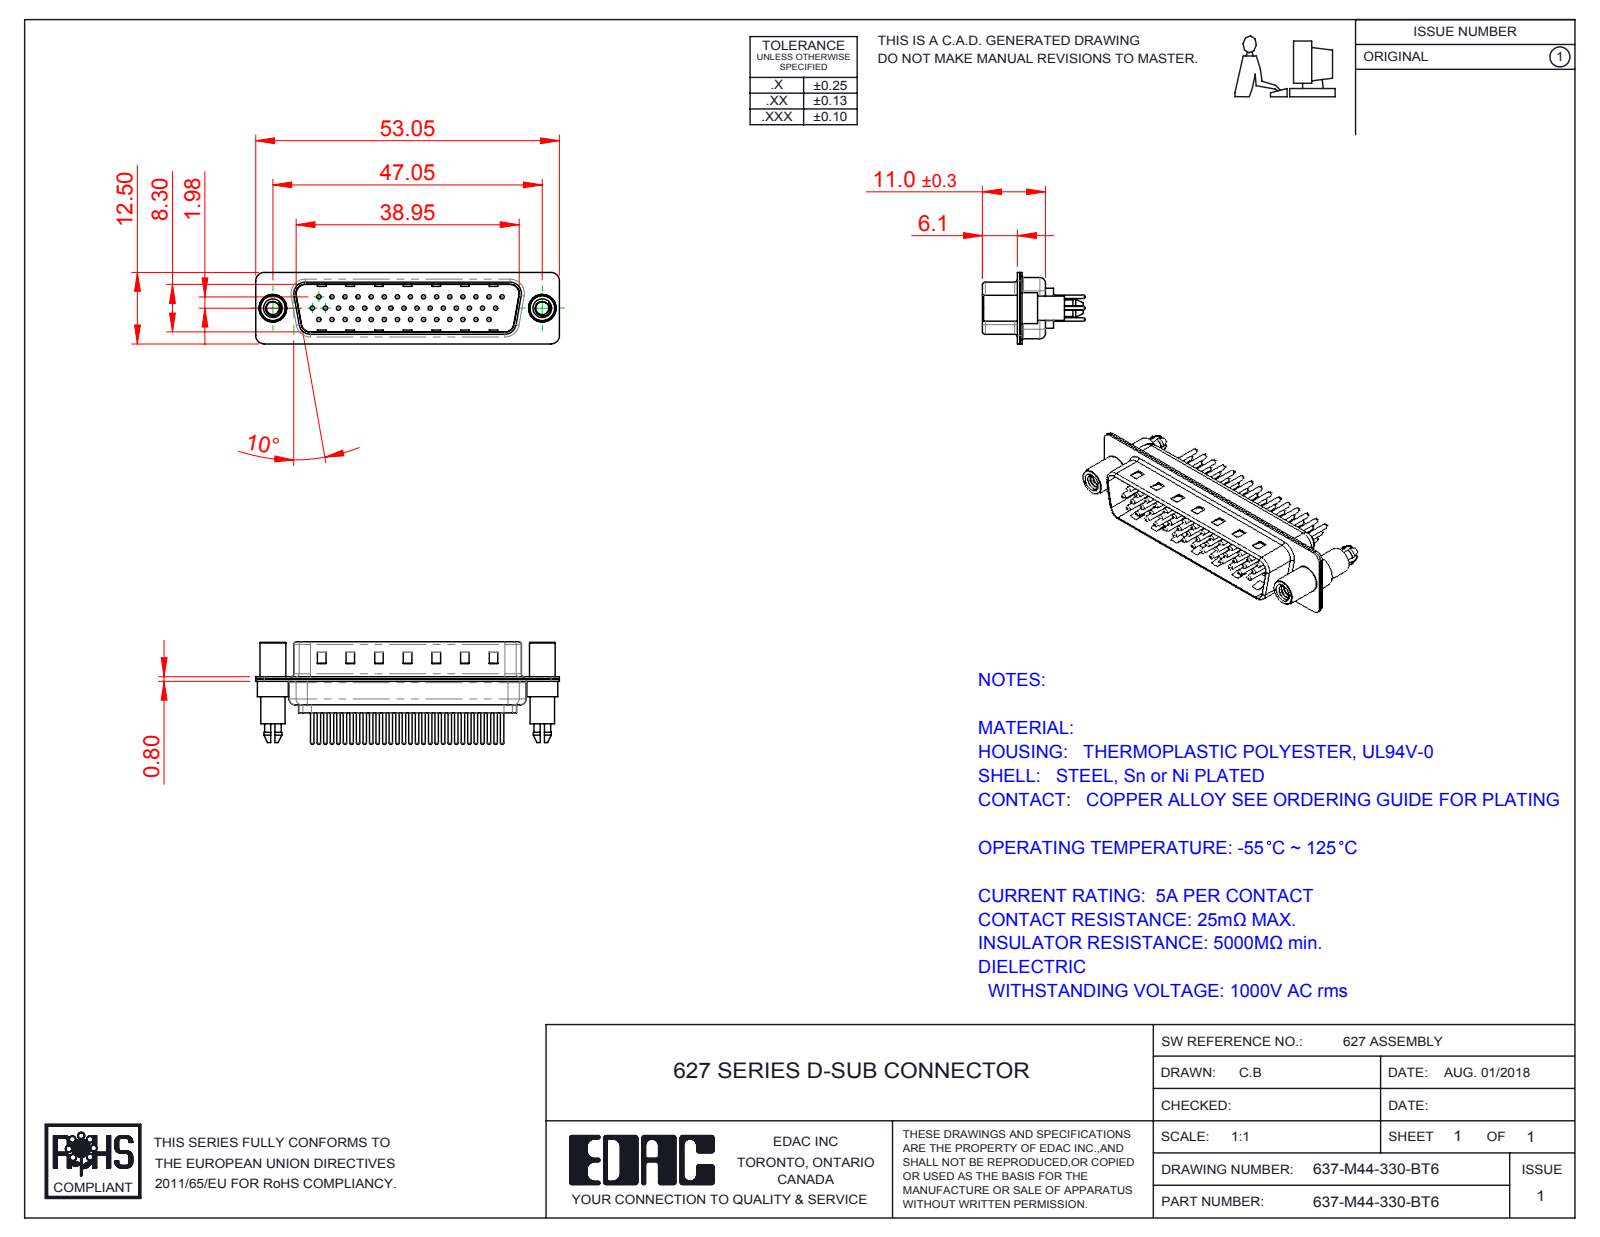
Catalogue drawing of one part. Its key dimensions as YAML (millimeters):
part_name: "637M 4-40 Threaded Standoff and Boardlock; 637M Housing_44 Contacts; 637M Contact Row 2_30; 637M Contact Row 1_30 (+4 more)"
step_written_by: "SolidWorks 2016 (CONFIG_CONTROL_DESIGN)"
units: millimeters
bodies: {solids: 49, faces: 2088, planar: 517, cylindrical: 789, other: 782}
overall_size: [53.05, 17.9, 12.5]
volume: 3165
surface_area: 8951
round_holes:
  - {diameter: 0.75, count: 44}
  - {diameter: 1.6, count: 44}
  - {diameter: 2, count: 44}
  - {diameter: 2.26, count: 2}
  - {diameter: 4, count: 2}
  - {diameter: 4.8, count: 2}
round_bosses_or_shafts:
  - {diameter: 1.5, count: 44}
  - {diameter: 0.6, count: 44}
  - {diameter: 2, count: 3}
  - {diameter: 0.75, count: 3}
  - {diameter: 5.4, count: 2}
  - {diameter: 4.9, count: 2}
  - {diameter: 4.5, count: 2}
  - {diameter: 4.25, count: 2}
partial_cylinders:
  - {radius: 1.5, count: 18}
  - {radius: 2, count: 12}
  - {radius: 1.6, count: 10}
  - {radius: 0.5, count: 8}
  - {radius: 0.25, count: 4}
  - {radius: 0.6, count: 4}
  - {radius: 0.65, count: 4}
  - {radius: 0.9, count: 4}
face_to_face_distances: [0.4, 0.8, 9.5, 9.1, 8.7, 9.9, 0.75, 6.3, 1.1, 0.35]
hole_center_spacings: [2.28, 3.96, 2.29, 4.57, 8.24, 6.86, 11.43, 14.99]
